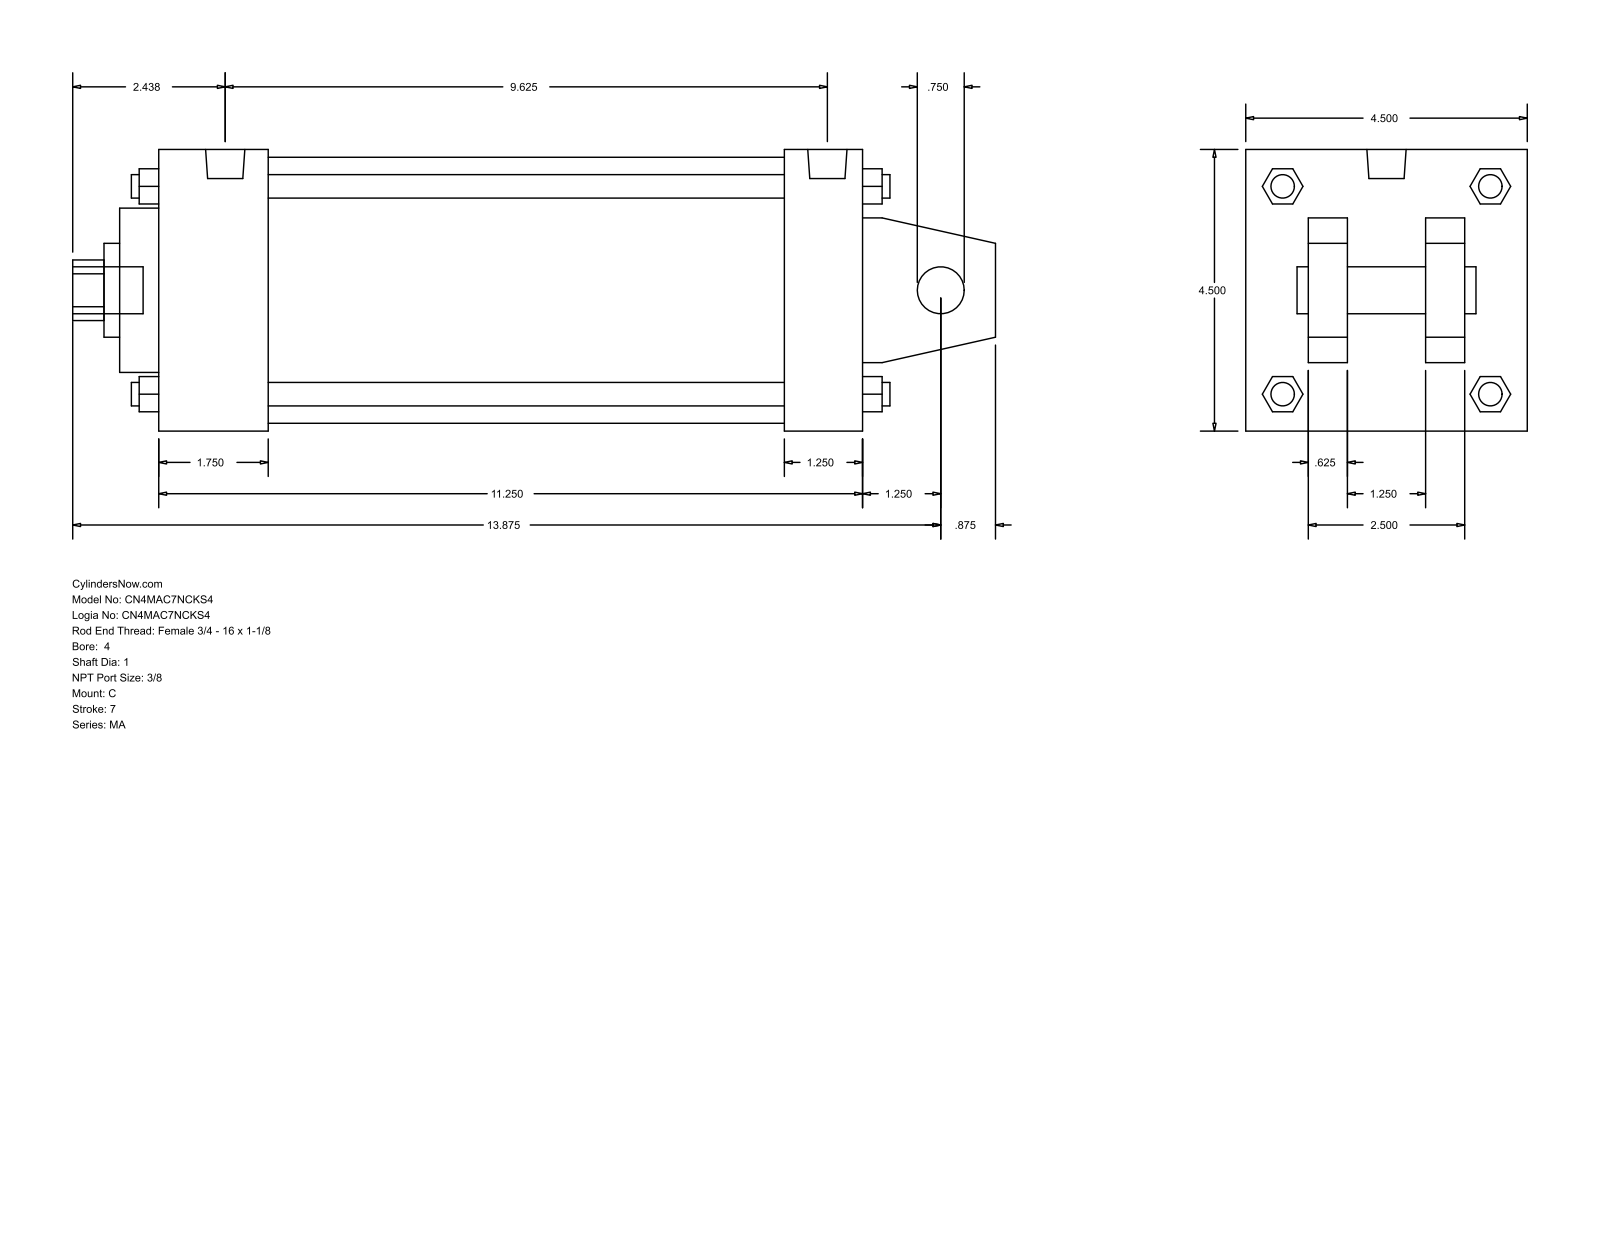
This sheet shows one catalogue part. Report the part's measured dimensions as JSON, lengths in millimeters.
{"part_name": "MA_C__0400_1", "step_written_by": "GSSL Pune (CONFIG_CONTROL_DESIGN)", "units": "millimeters", "bodies": {"solids": 0, "faces": 141, "planar": 109, "cylindrical": 32, "other": 0}, "overall_size": [374.65, 114.3, 114.3], "round_holes": [[19.05, 1], [25.4, 1], [38.1, 1], [66.67, 1], [107.95, 1]], "round_bosses_or_shafts": [[11.11, 4], [9.53, 4], [15.93, 2], [19.05, 1]], "partial_cylinders_radius": [[12.29, 1]], "face_to_face_distances": [114.3, 285.76, 15.87, 73.03, 41.27, 25.4, 88.9, 47.63, 254.01, 31.75]}
